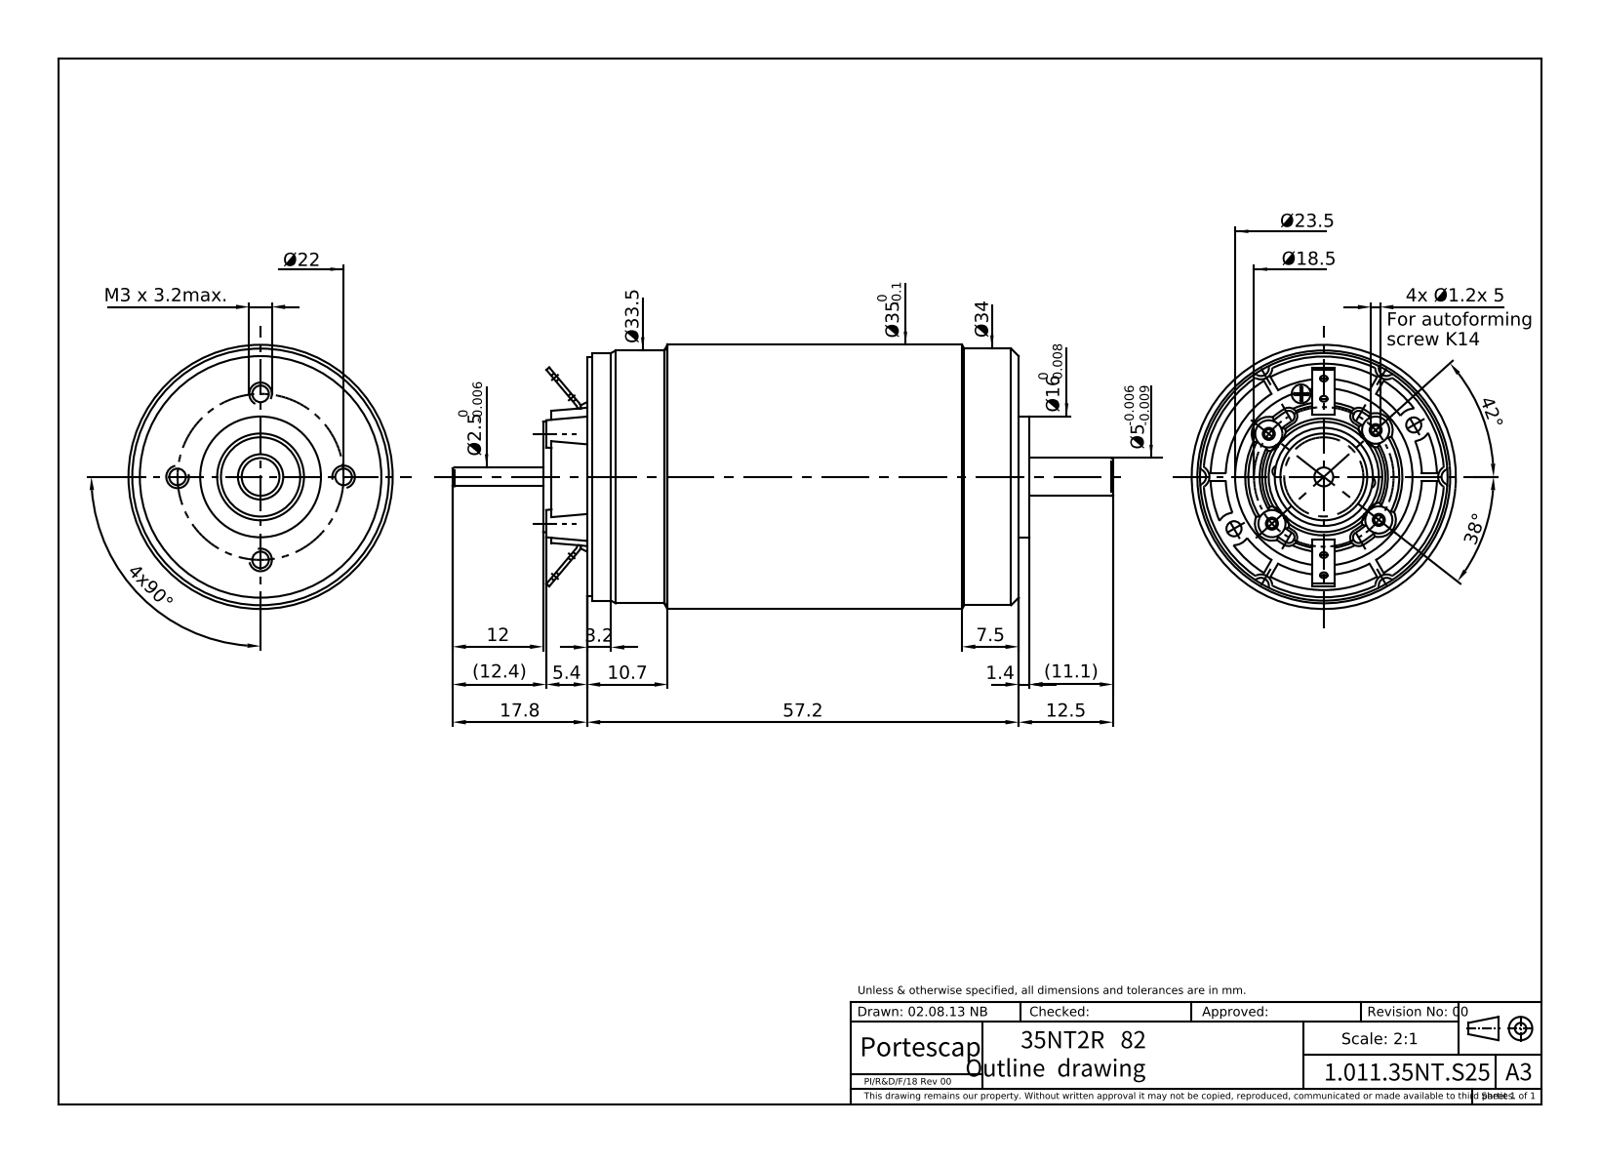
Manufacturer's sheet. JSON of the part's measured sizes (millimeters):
{"part_name": "35NT2R82_1", "step_written_by": "PRO/ENGINEER BY PARAMETRIC TECHNOLOGY CORPORATION, 2014310 (CONFIG_CONTROL_DESIGN)", "units": "millimeters", "bodies": {"solids": 1, "faces": 247, "planar": 86, "cylindrical": 95, "other": 66}, "overall_size": [76.07, 35, 35], "volume_mm3": 54841, "surface_area_mm2": 9551, "round_holes": [[1.6, 6], [2.5, 5], [1, 4], [1.2, 4], [3, 4], [2, 2], [5, 1], [13, 1]], "round_bosses_or_shafts": [[35, 1], [34, 1], [33.5, 1], [32.8, 1], [31.8, 1], [16, 1]], "partial_cylinders_radius": [[2.1, 6], [0.2, 4], [10, 4], [2.15, 2], [0.6, 1]], "face_to_face_distances": [0.5, 57.2, 56.7, 1.4, 58.1, 58.6, 59.56, 58.16, 1.46, 0.96], "hole_center_spacings": [9.25, 11, 15.56, 18.51, 3.5, 5.05, 5.52, 5.62]}
